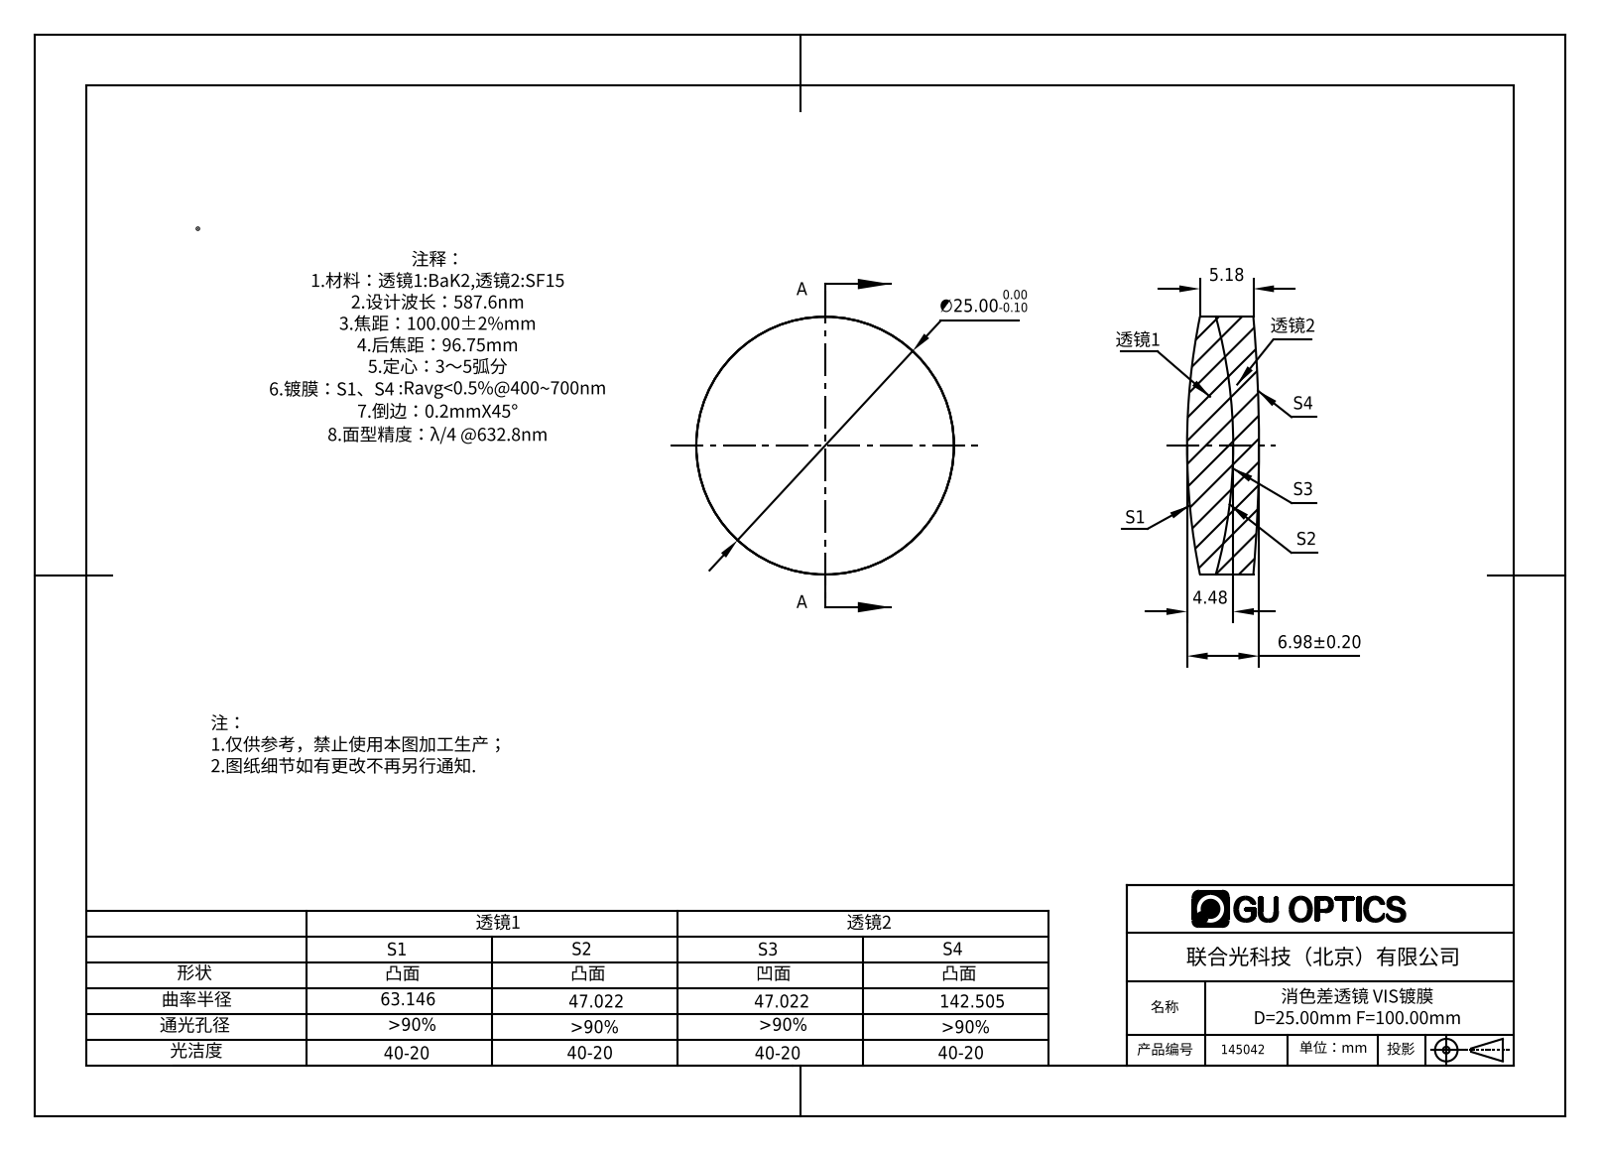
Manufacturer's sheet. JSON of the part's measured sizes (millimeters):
{"part_name": "145042", "step_written_by": "SolidWorks 2016 (AUTOMOTIVE_DESIGN)", "units": "millimeters", "bodies": {"solids": 2, "faces": 12, "planar": 0, "cylindrical": 4, "other": 8}, "overall_size": [25, 25, 6.98], "volume_mm3": 2986, "surface_area_mm2": 2394, "round_bosses_or_shafts": [[25, 1]]}
